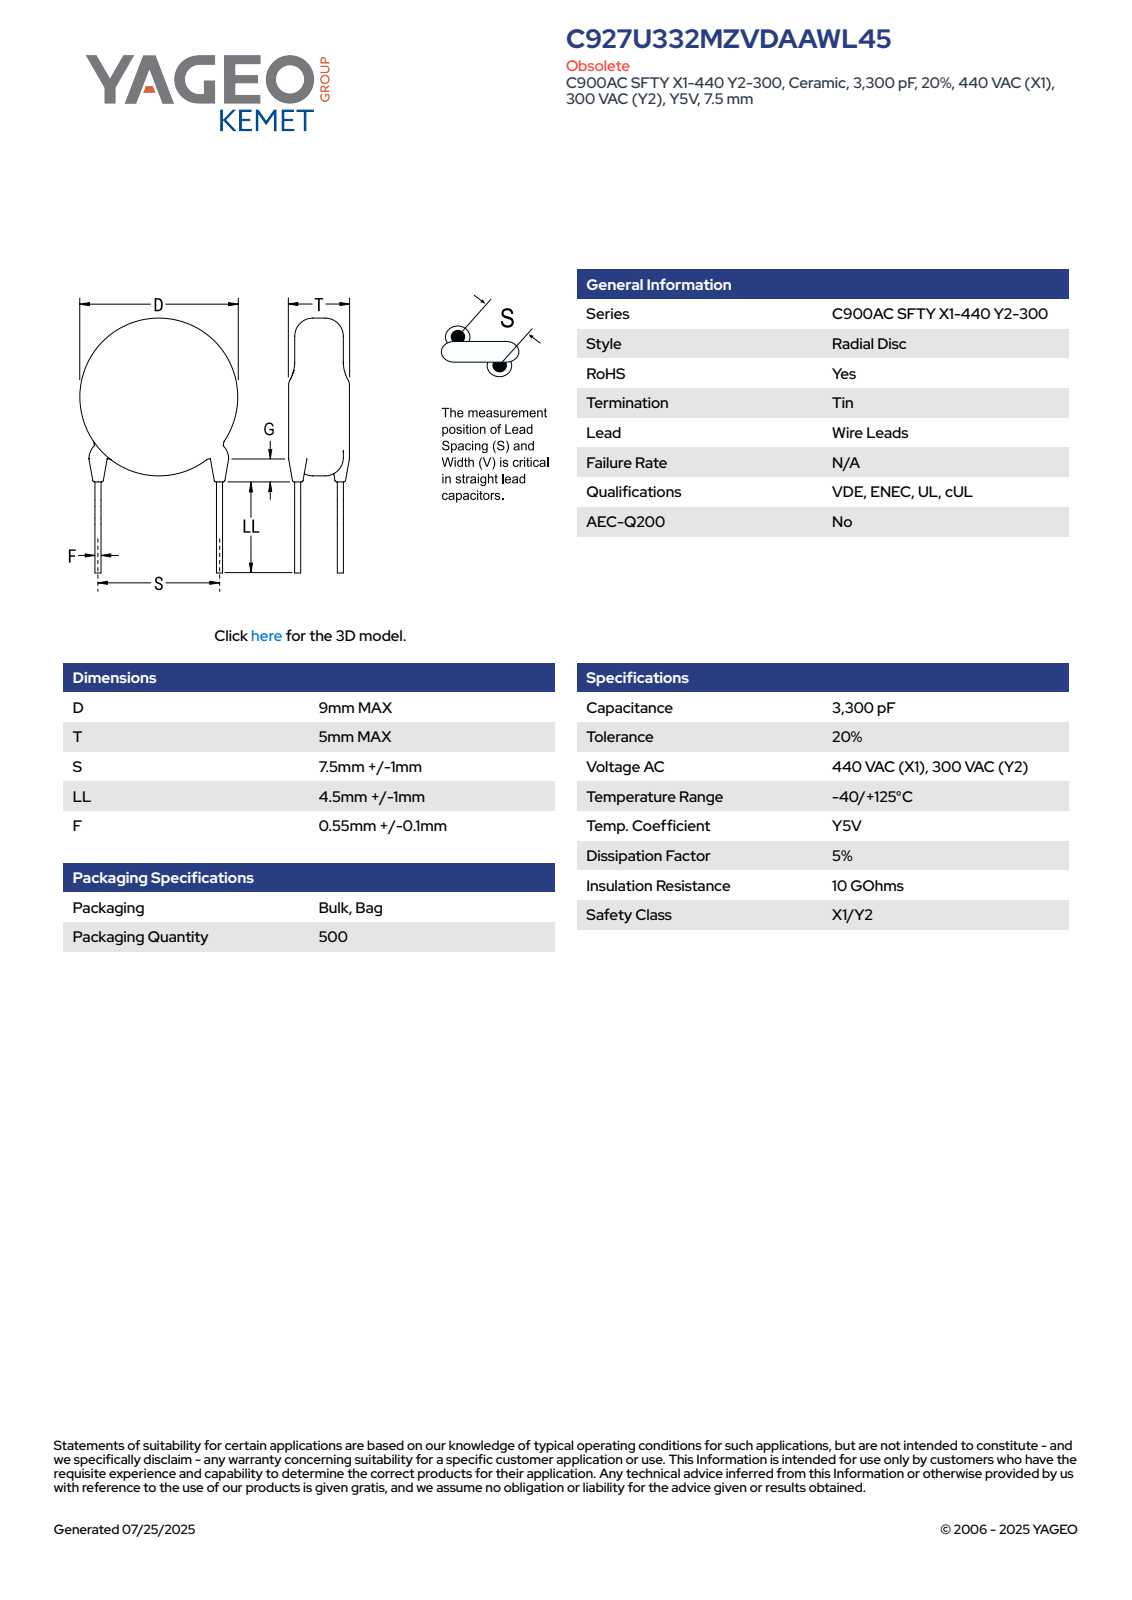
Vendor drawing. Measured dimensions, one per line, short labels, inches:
name: CCD_STC900_D9T5S7.5LL5.5F0.65G3
written by: SolidWorks 2014 (AUTOMOTIVE_DESIGN)
unit: in
bodies: 4 solids, 83 faces (61 planar, 6 cylindrical, 16 other)
size: 0.583 × 0.354 × 0.197
volume: 0.019 in³; area: 0.436 in²
bosses: 2× ⌀0.026, 1× ⌀0.354
face distances: 0.197, 0.041, 0.426, 0.385, 0.033, 0.018, 0.015, 0.084, 0.121, 0.126
